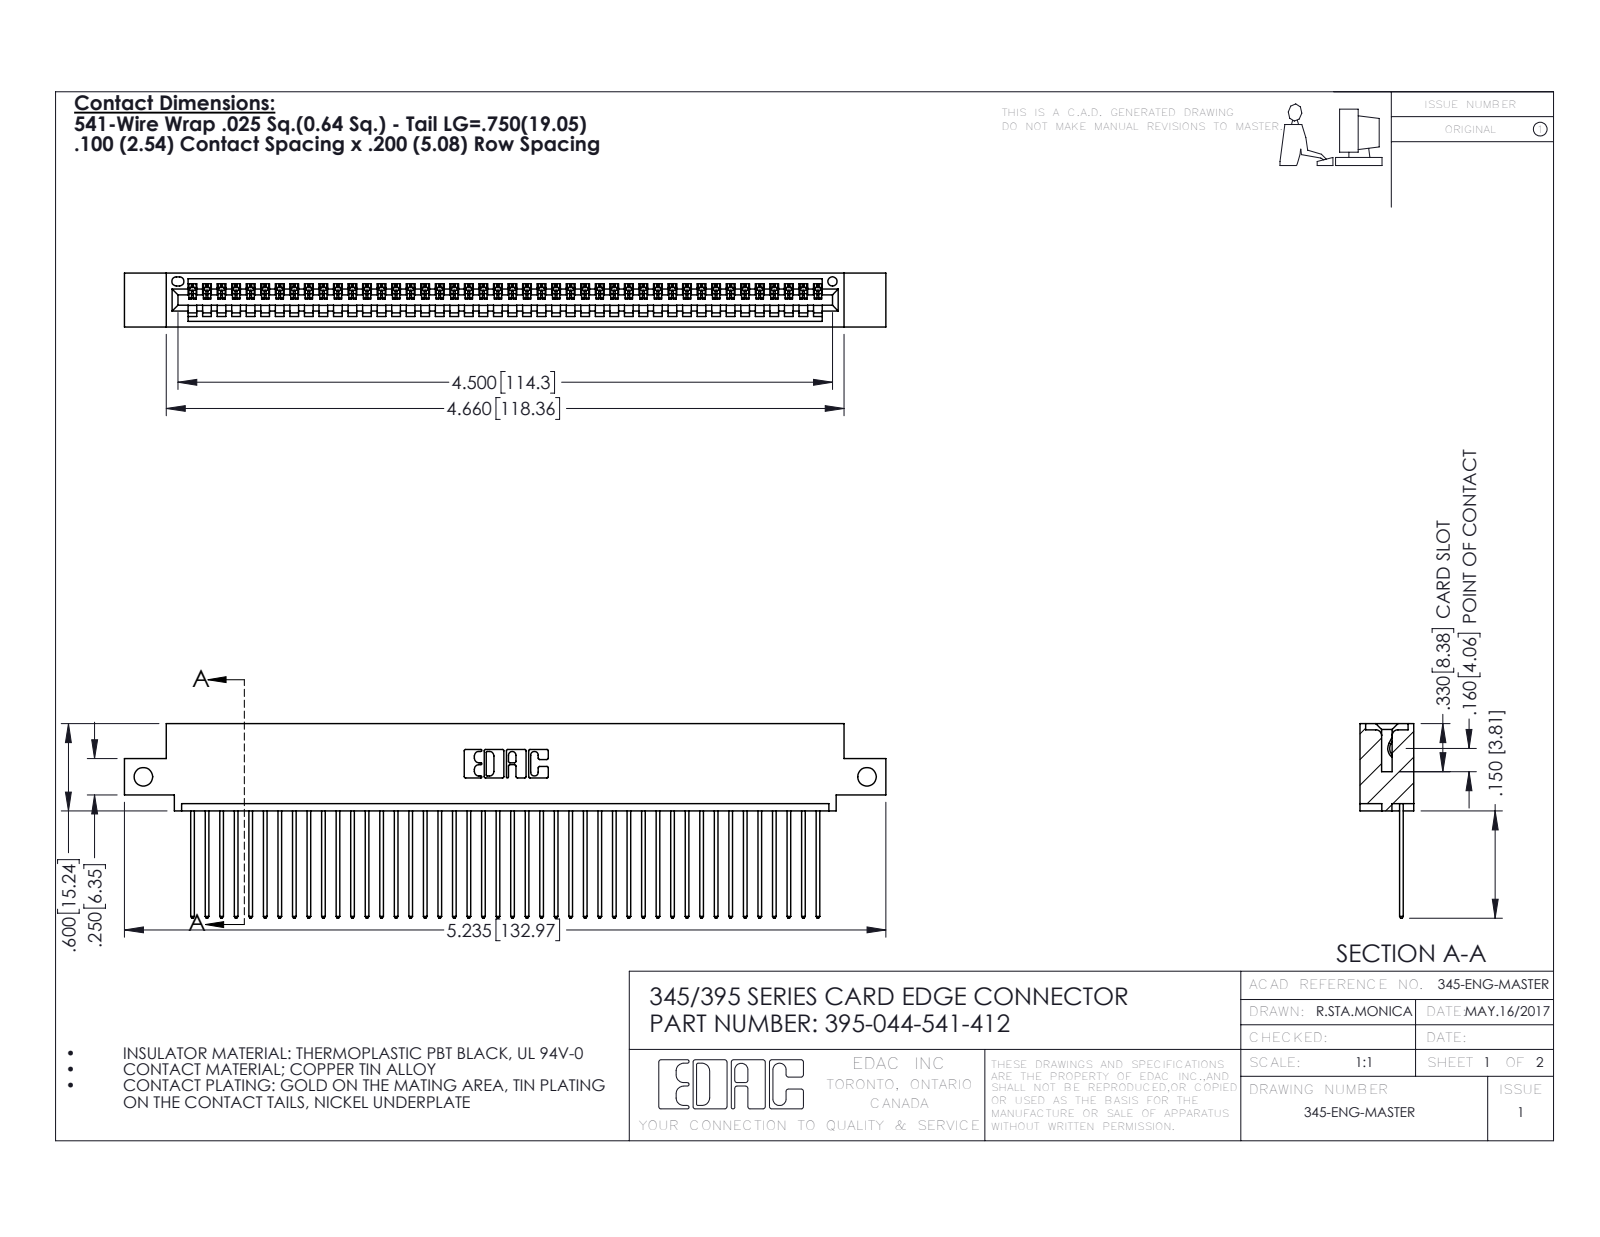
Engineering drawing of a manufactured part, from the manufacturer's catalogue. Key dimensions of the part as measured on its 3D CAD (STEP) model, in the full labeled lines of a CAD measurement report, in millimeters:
Part name (STEP PRODUCT): 345-292-001_345-293-141; 395-044-541-412; 345 Part_0.110 Offset - Side Mount
STEP written by: SolidWorks 2016 (CONFIG_CONTROL_DESIGN)
Units: millimetres
Bodies: 45 solids, 2682 faces (1844 planar, 838 cylindrical, 0 other)
Overall size (bounding box): 133 × 34 × 9.4
Volume: 12 600 mm³ · Surface area: 17 610 mm²
Round holes (diameter × count): ⌀3.3 ×2, ⌀1.6 ×1
Partial cylindrical surfaces — rounded edges, fillets, slot ends (radius × count): R0.2 ×88, R0.3 ×88, R0.3 ×22, R0.2 ×6, R0.8 ×6, R0.7 ×3, R0.8 ×2, R1 ×2
Main face-to-face distances: 1.8, 7.6, 2.5, 6.9, 0.6, 9.4, 5.1, 5.7, 3.8, 1.8
Hole centre spacings: 126.4
